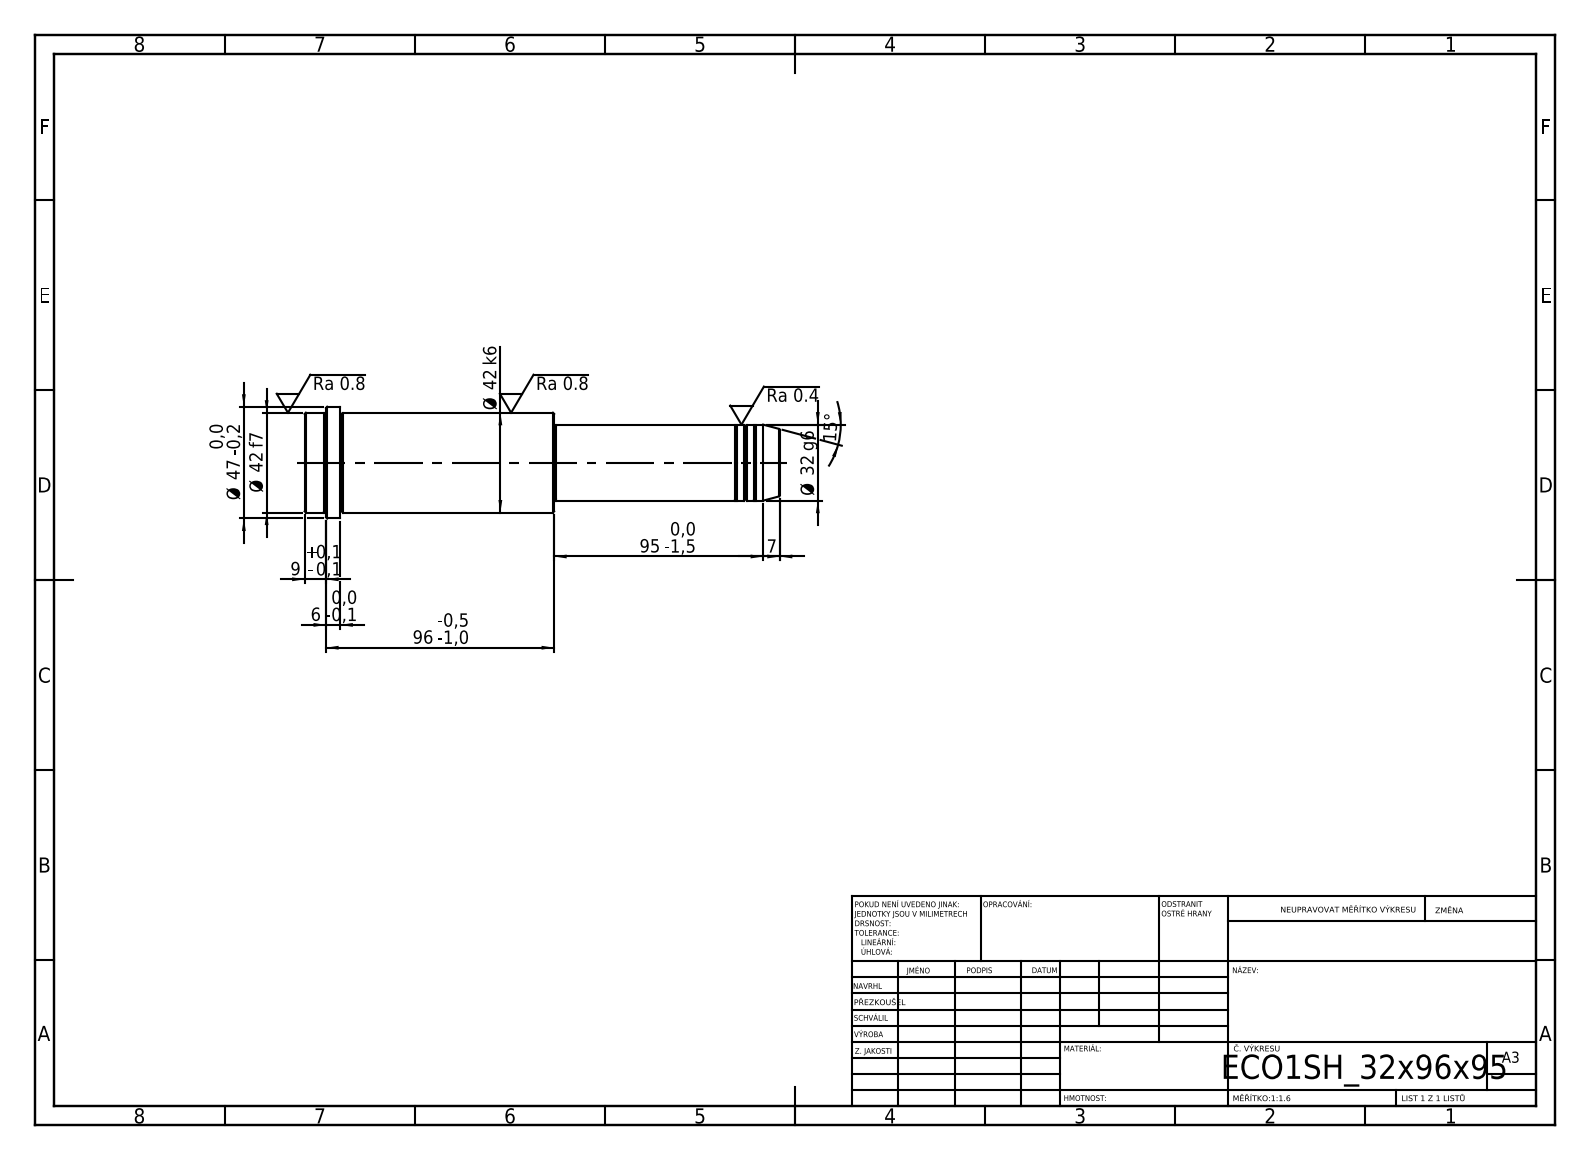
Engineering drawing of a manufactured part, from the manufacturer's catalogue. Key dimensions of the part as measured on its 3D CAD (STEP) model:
STEP written by: SolidWorks 2019 (CONFIG_CONTROL_DESIGN)
Units: millimetres
Bodies: 1 solid, 52 faces (6 planar, 16 cylindrical, 30 other)
Overall size (bounding box): 200 × 47 × 47
Volume: 223 015 mm³ · Surface area: 27 045 mm²
Round bosses / shafts (diameter × count): ⌀47 ×1, ⌀42 ×1, ⌀32 ×1, ⌀31 ×1
Main face-to-face distances: 200, 95, 105, 185, 90, 15, 191, 96, 6, 9
